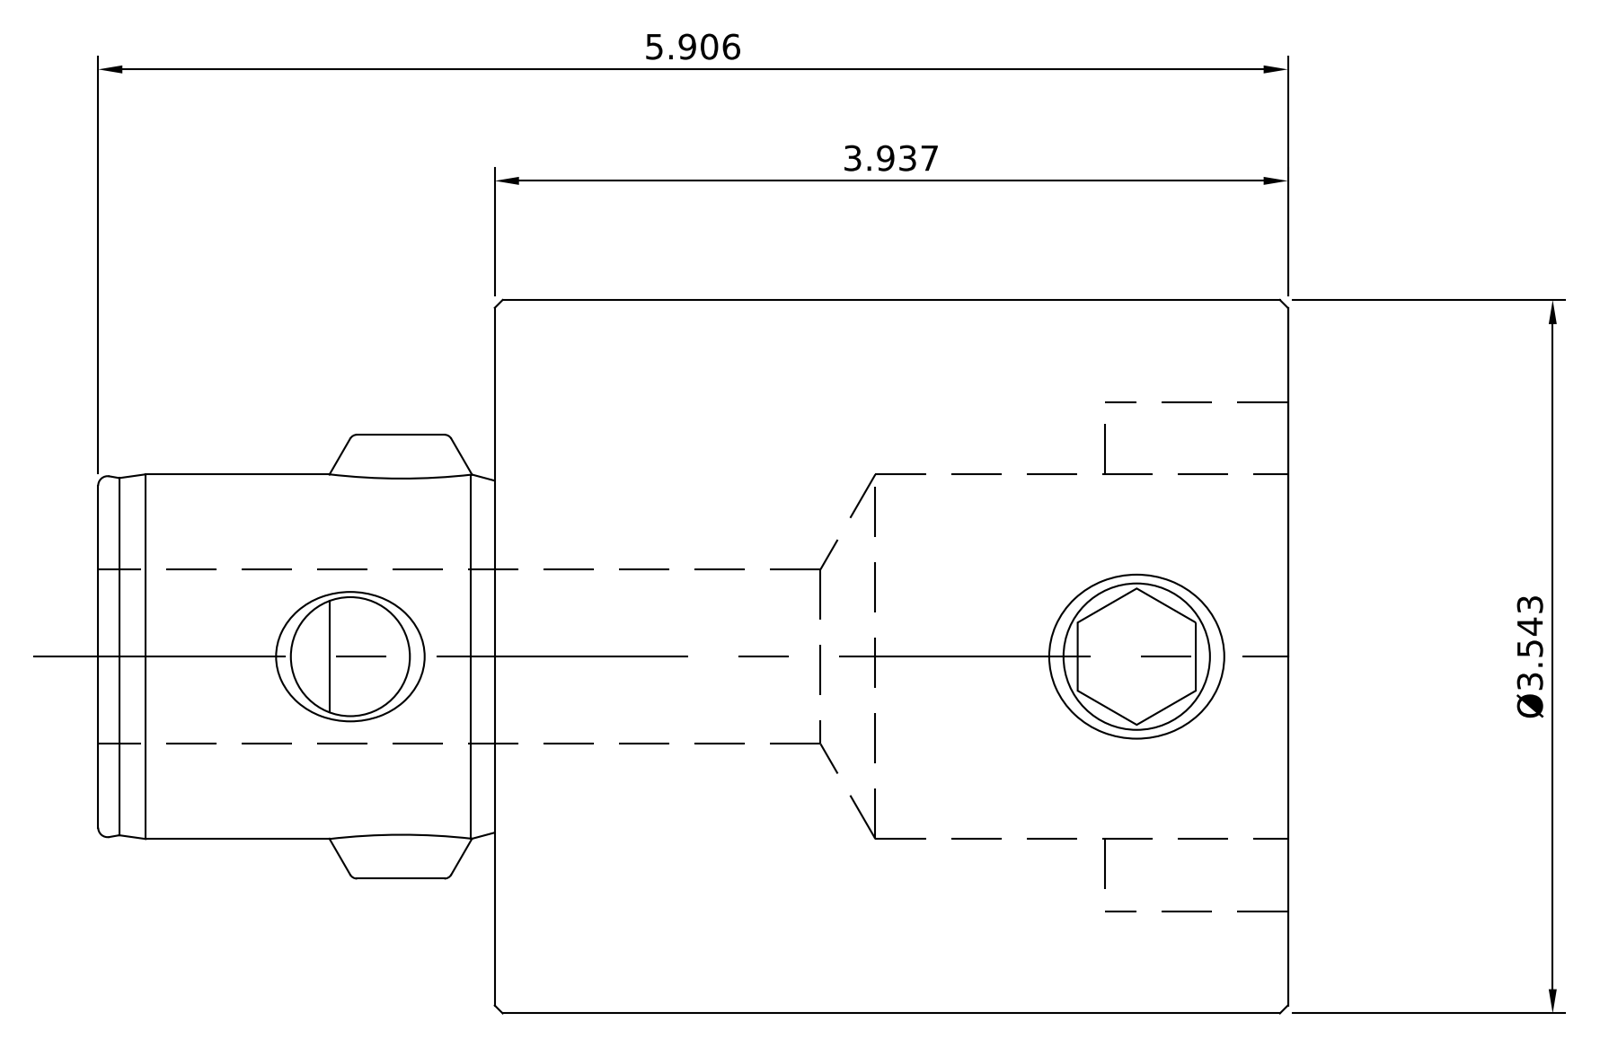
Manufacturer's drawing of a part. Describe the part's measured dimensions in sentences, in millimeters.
The part is named "691-50XRing_10.691.507Ring; 11.331.770; 10.691.50X_10.691.507; 10.690.43X_10.690.437 (+1 more)". Its 3-D file was written by "SolidWorks 2016 (AUTOMOTIVE_DESIGN)". It is 4 solids with 142 faces: 39 planar, 47 cylindrical and 56 other. Overall it measures 150 by 90 by 90 millimeters. Its volume is 562 122 cubic millimeters and its surface area 72 193 square millimeters. Round holes: 1 of diameter 8, 1 of diameter 15, 1 of diameter 17.5, 1 of diameter 18, 1 of diameter 21, 1 of diameter 22, 1 of diameter 24.7, 1 of diameter 36, 1 of diameter 46, 1 of diameter 47. Round bosses or shafts: 1 of diameter 90, 1 of diameter 89.6, 1 of diameter 20, 1 of diameter 17.9, 1 of diameter 15.9, 1 of diameter 12. Partial cylindrical surfaces (rounded edges, fillets, slot ends): 2 of radius 7, 1 of radius 23. The main face-to-face distances are 100, 50, 150, 94, 44, 56, 39.14, 128, 78, 34. The hole center spacings are 34, 99.15.
